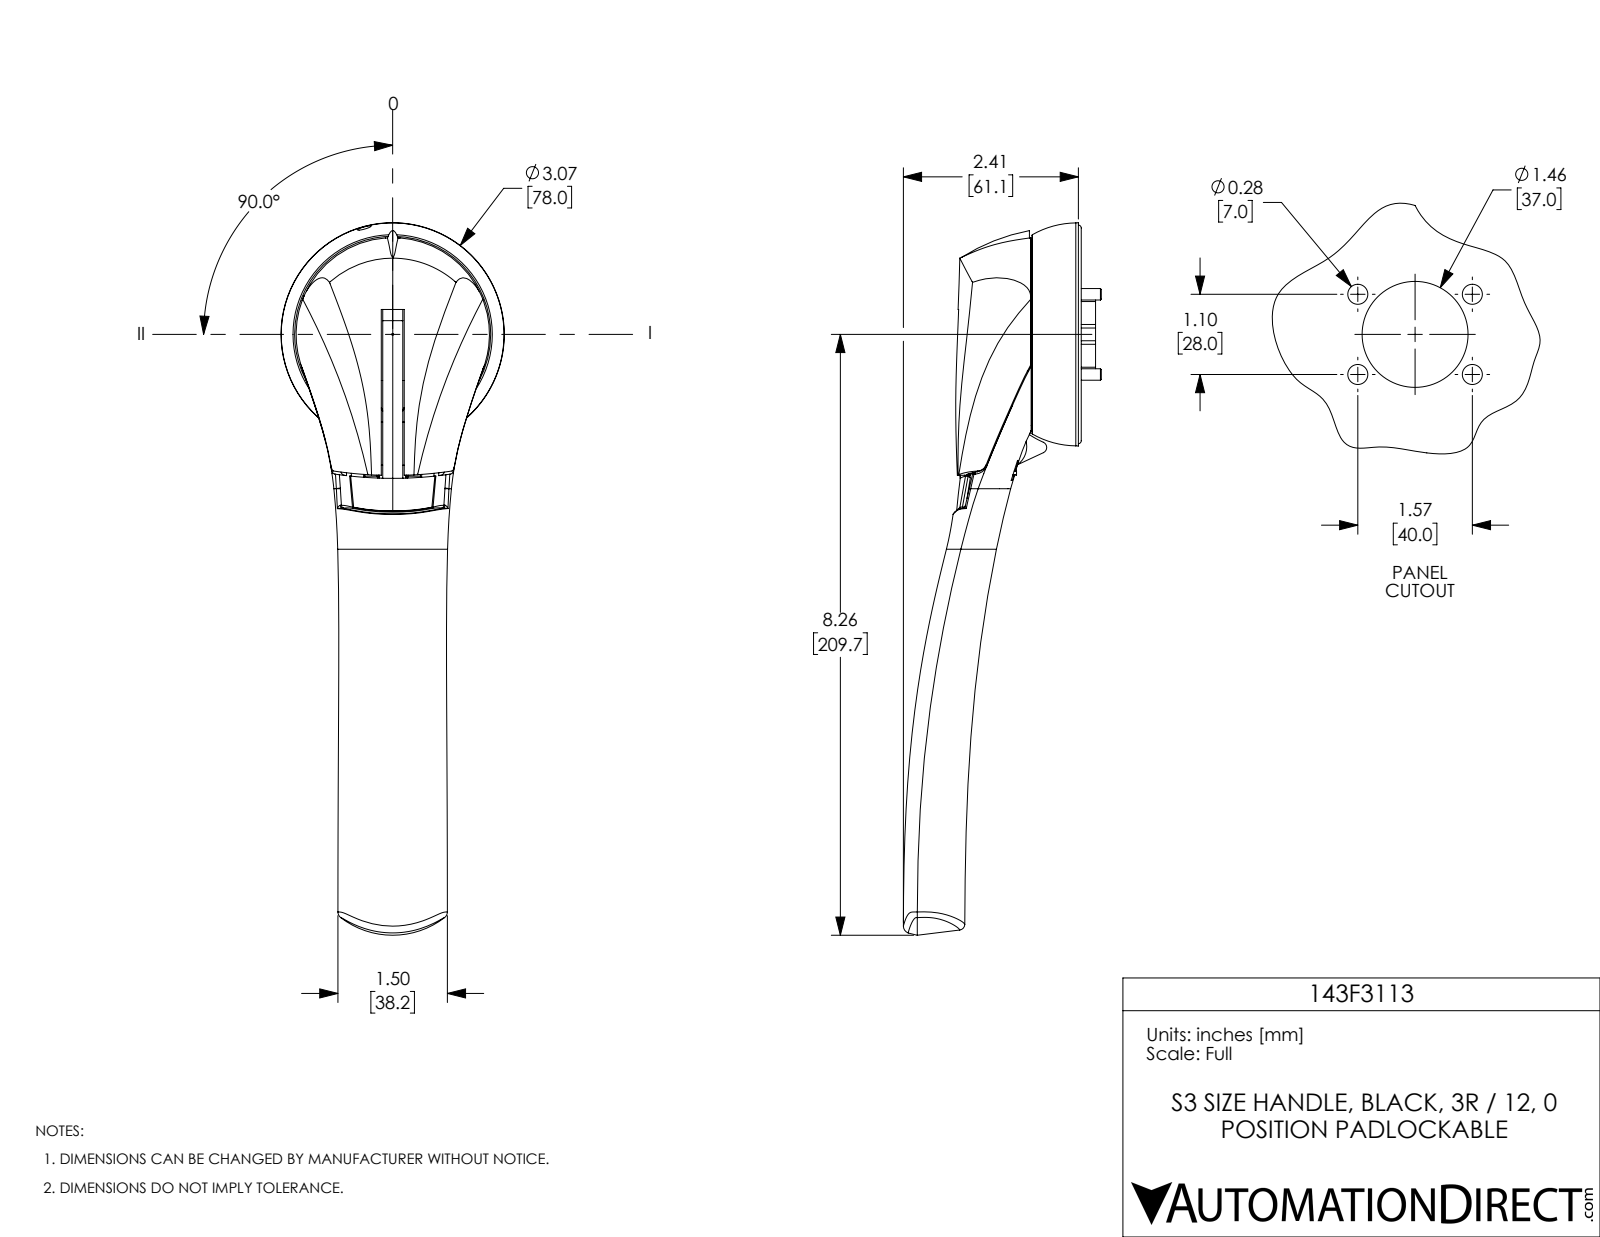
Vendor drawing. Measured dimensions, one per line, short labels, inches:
name: 143F3113
written by: SolidWorks 2017 (AUTOMOTIVE_DESIGN)
unit: in
bodies: 8 solids, 1514 faces (806 planar, 544 cylindrical, 164 other)
size: 9.793 × 3.07 × 2.721
volume: 12.91 in³; area: 100.4 in²
holes: 6× ⌀0.157, 4× ⌀0.339, 4× ⌀0.425, 3× ⌀0.03, 2× ⌀0.169, 2× ⌀0.362, 1× ⌀0.118, 1× ⌀0.189, 1× ⌀2.992
bosses: 11× ⌀0.02, 4× ⌀0.335, 4× ⌀0.315, 3× ⌀0.089, 3× ⌀0.069, 2× ⌀0.228, 1× ⌀2.819, 1× ⌀2.701
rounds: 221× R0.01, 20× R0.015, 20× R0.034, 15× R0.03, 4× R0.039, 3× R0.025, 3× R5.437, 2× R0.079
face distances: 0.024, 0.701, 0.713, 0.689, 0.035, 0.276, 0.102, 0.173, 0.244, 0.047
hole spacings: 0.961, 0.309, 0.669, 1.098, 1.102, 1.203, 1.575, 1.881
